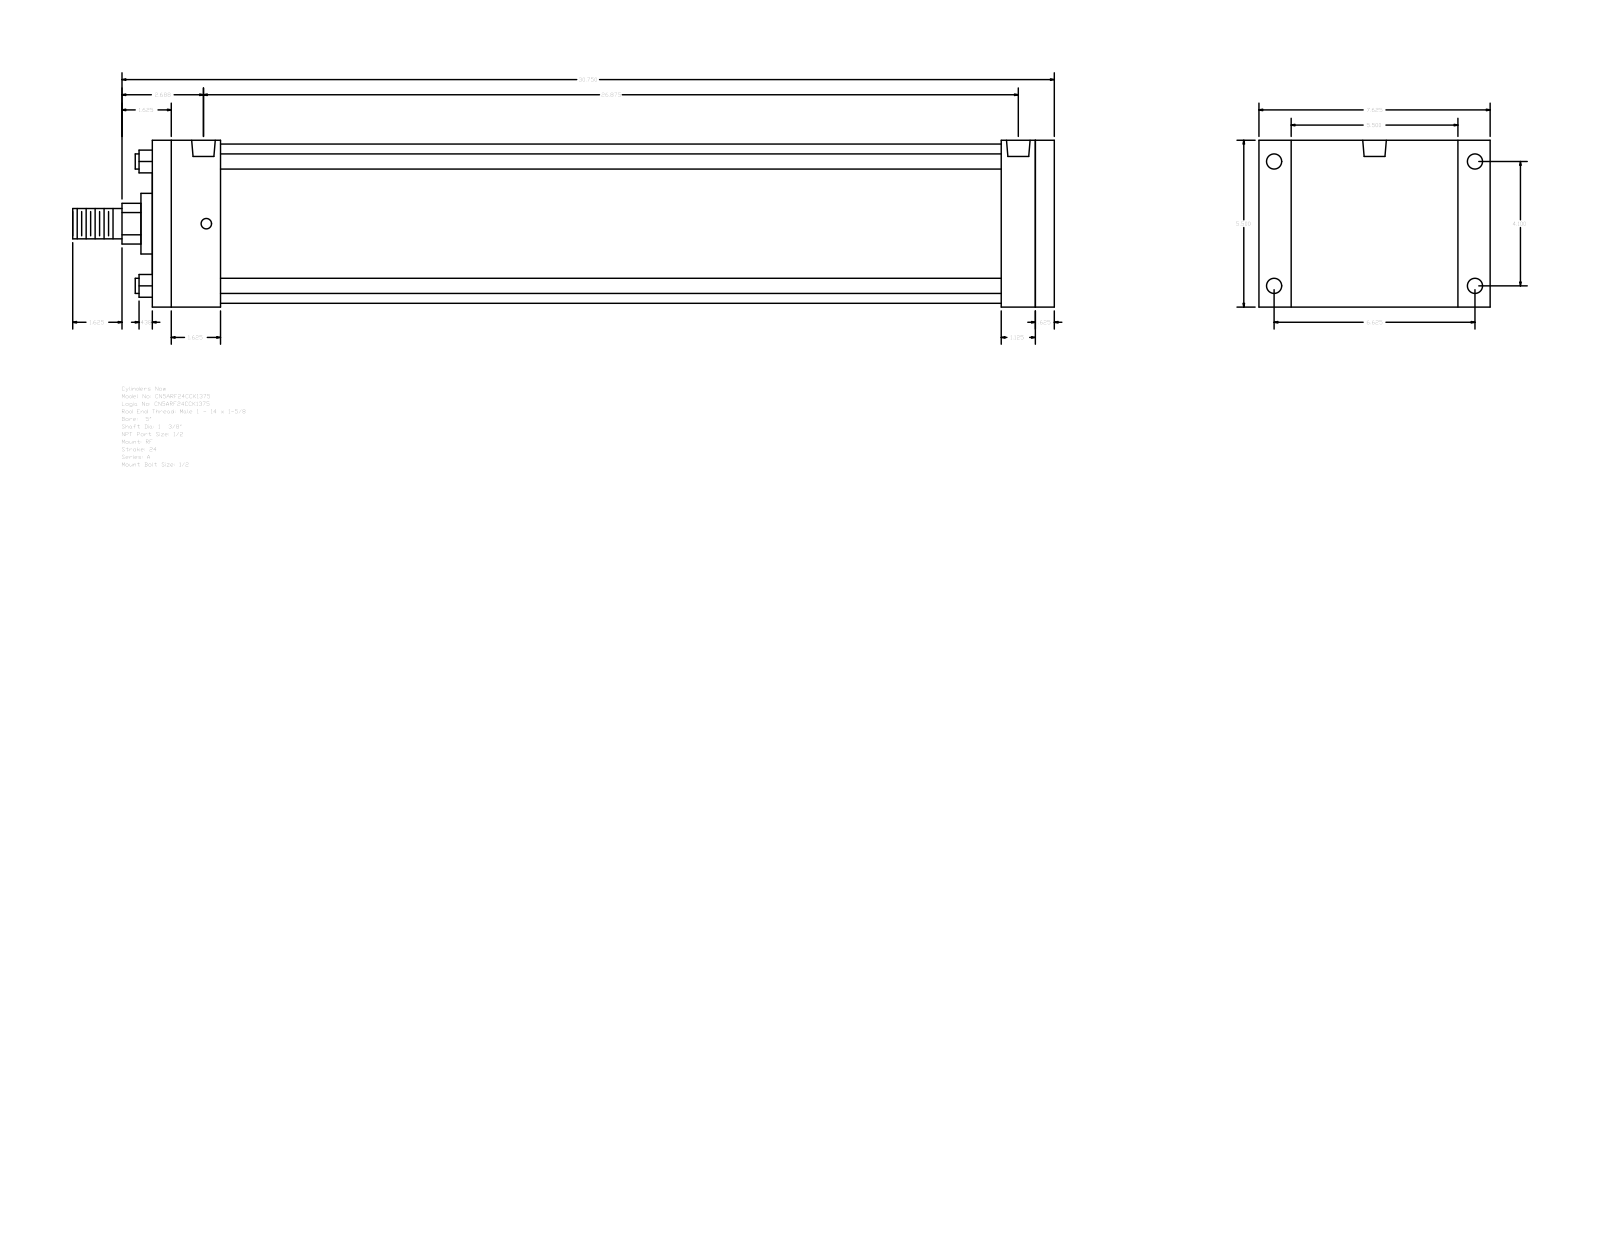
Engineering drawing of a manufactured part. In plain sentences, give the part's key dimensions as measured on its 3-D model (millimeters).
The part is named "A_RF__0500_1.375". Its 3-D file was written by "GSSL Pune (CONFIG_CONTROL_DESIGN)". It is 0 solids with 92 faces: 64 planar, 28 cylindrical and 0 other. Overall it measures 822.33 by 193.68 by 139.7 millimeters. Round holes: 4 of diameter 8.73, 4 of diameter 12.7, 2 of diameter 19.77. Round bosses or shafts: 4 of diameter 12.7, 1 of diameter 133.35, 1 of diameter 50.8, 1 of diameter 34.92, 1 of diameter 25.4. Partial cylindrical surfaces (rounded edges, fillets, slot ends): 1 of radius 17.06. The main face-to-face distances are 139.7, 755.65, 15.88, 739.77, 57.15, 682.62, 698.5, 711.2, 654.05, 28.57. The hole center spacings are 2.39, 104.14, 168.28, 197.9, 677.85, 680.24, 682.63.
